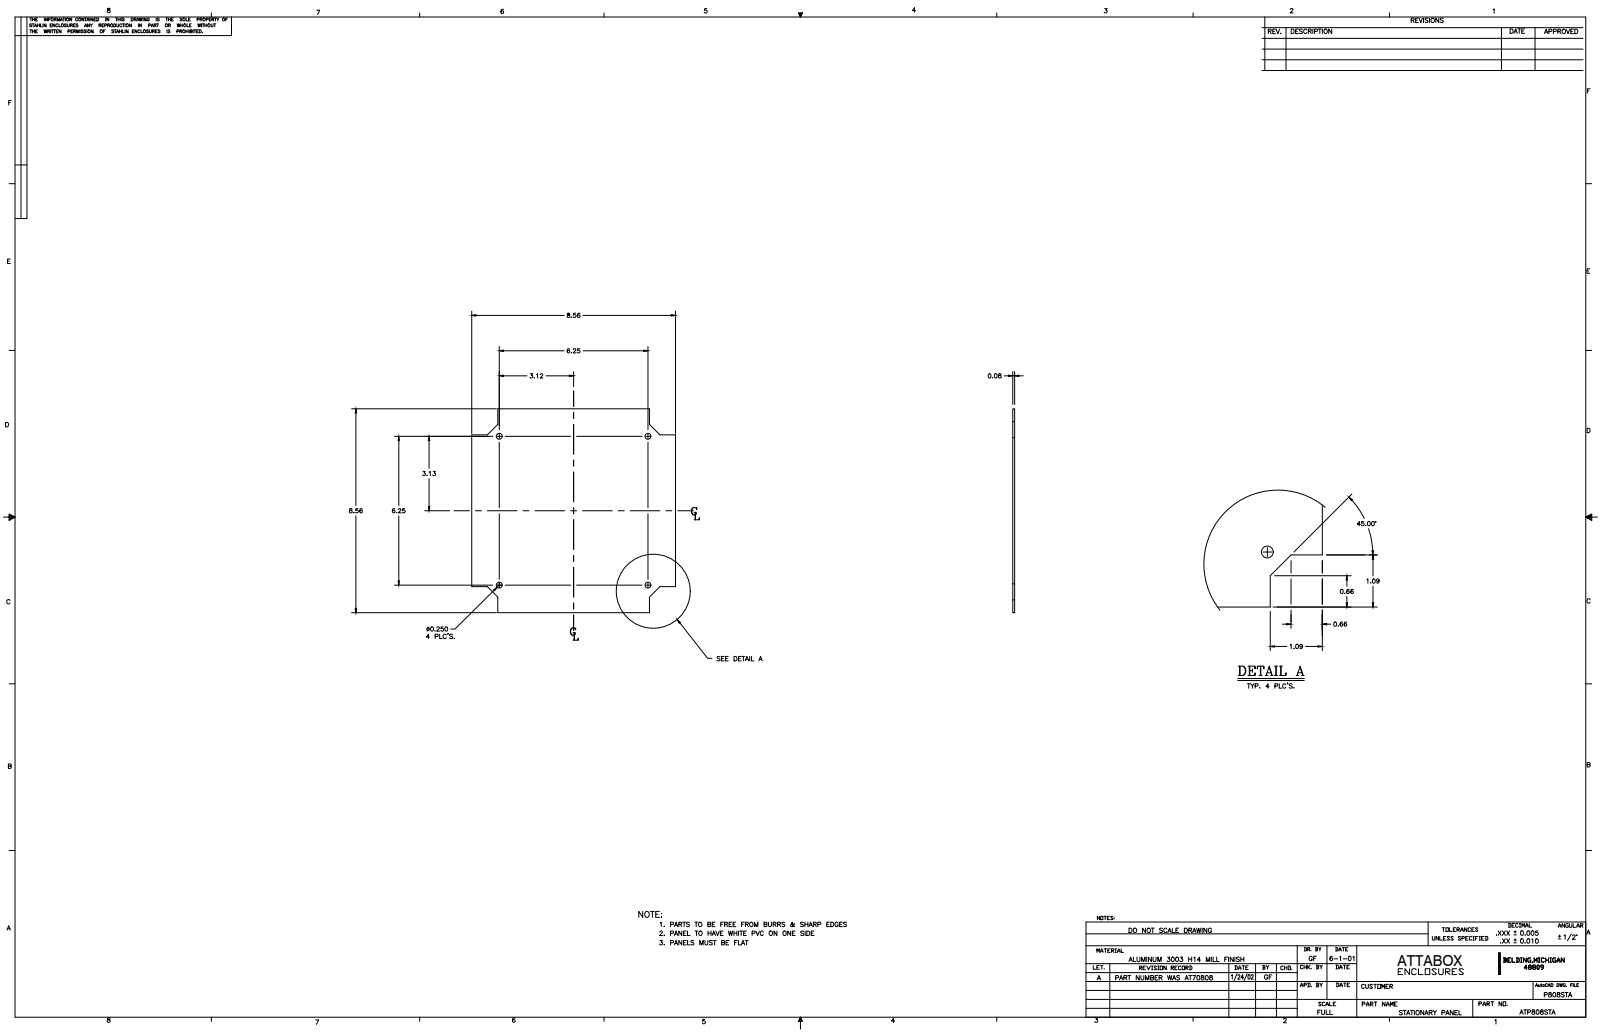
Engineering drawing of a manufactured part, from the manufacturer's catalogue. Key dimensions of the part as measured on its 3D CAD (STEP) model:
Part name (STEP PRODUCT): P808STAL
STEP written by: Autodesk Inventor 11 (AUTOMOTIVE_DESIGN)
Units: inches
Bodies: 1 solid, 22 faces (18 planar, 4 cylindrical, 0 other)
Overall size (bounding box): 8.563 × 8.563 × 0.08
Volume: 5.497 in³ · Surface area: 140.3 in²
Round holes (diameter × count): ⌀0.25 ×4
Main face-to-face distances: 0.08, 8.562, 1.094, 7.468, 6.374, 9.631
Hole centre spacings: 6.25, 8.839
